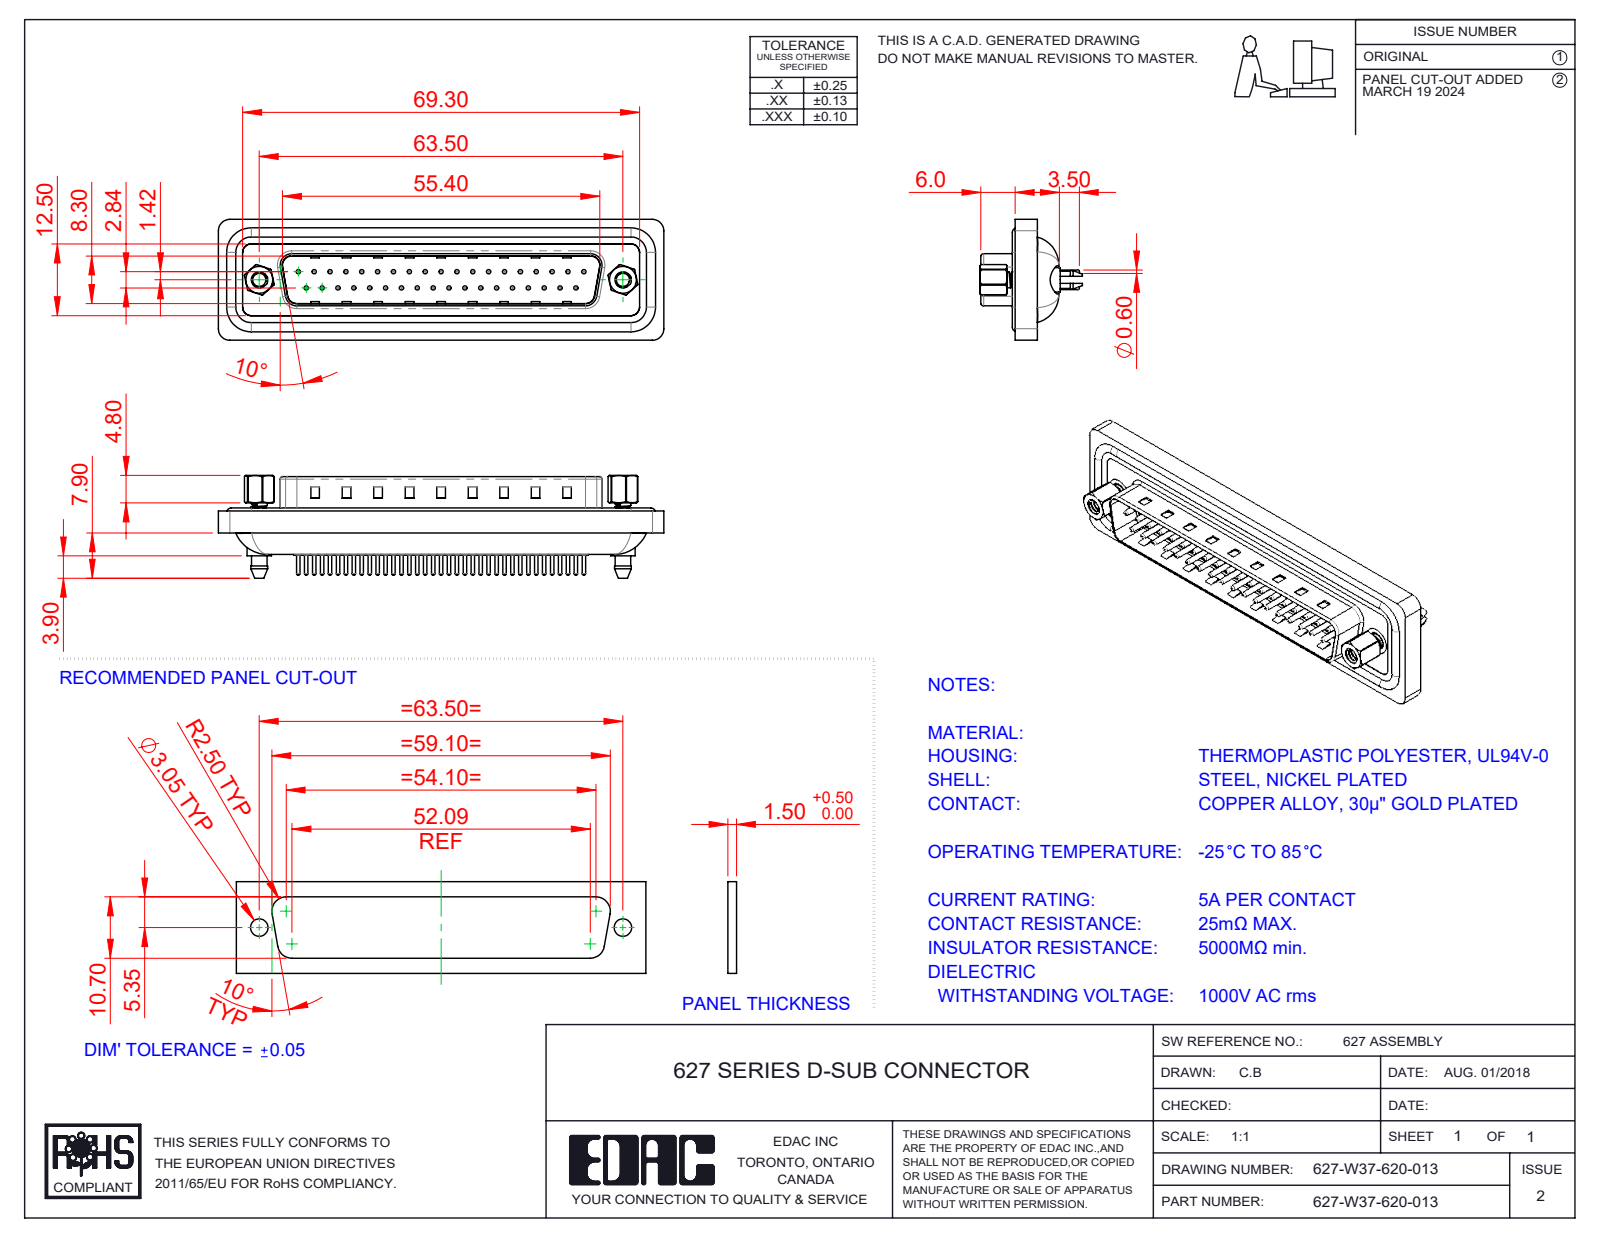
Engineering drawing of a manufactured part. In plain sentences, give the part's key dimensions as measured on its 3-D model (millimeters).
The part is named "627W Contact Row 1_20; 627W Waterproof Housing_37 Contacts BL; 627W 4-40 Threaded Boardlock; 627W Shell Front_37 Contacts (+4 more)". Its 3-D file was written by "SolidWorks 2023 (CONFIG_CONTROL_DESIGN)". It is 45 solids with 2047 faces: 510 planar, 848 cylindrical and 689 other. Overall it measures 77.8 by 21.1 by 17.95 millimeters. Its volume is 9 541 cubic millimeters and its surface area 14 743 square millimeters. Round holes: 37 of diameter 0.75, 37 of diameter 1.5, 37 of diameter 1.6, 37 of diameter 2, 2 of diameter 2.26, 2 of diameter 2.29, 2 of diameter 4, 2 of diameter 4.8, 2 of diameter 5. Round bosses or shafts: 37 of diameter 0.6, 9 of diameter 1.5, 4 of diameter 1.6, 2 of diameter 5.4, 2 of diameter 4.9, 2 of diameter 4.25, 2 of diameter 2.79. Partial cylindrical surfaces (rounded edges, fillets, slot ends): 16 of radius 1.5, 16 of radius 2, 8 of radius 0.5, 6 of radius 1.6, 4 of radius 0.9, 4 of radius 2.7, 4 of radius 4.3, 2 of radius 0.4. The main face-to-face distances are 0.75, 0.4, 4.1, 1.1, 2.75, 5.65, 4.6, 15.45, 3.75, 14.7. The hole center spacings are 3.16, 2.77, 5.54, 8.31, 5.04, 10.1, 11.08, 12.78.
